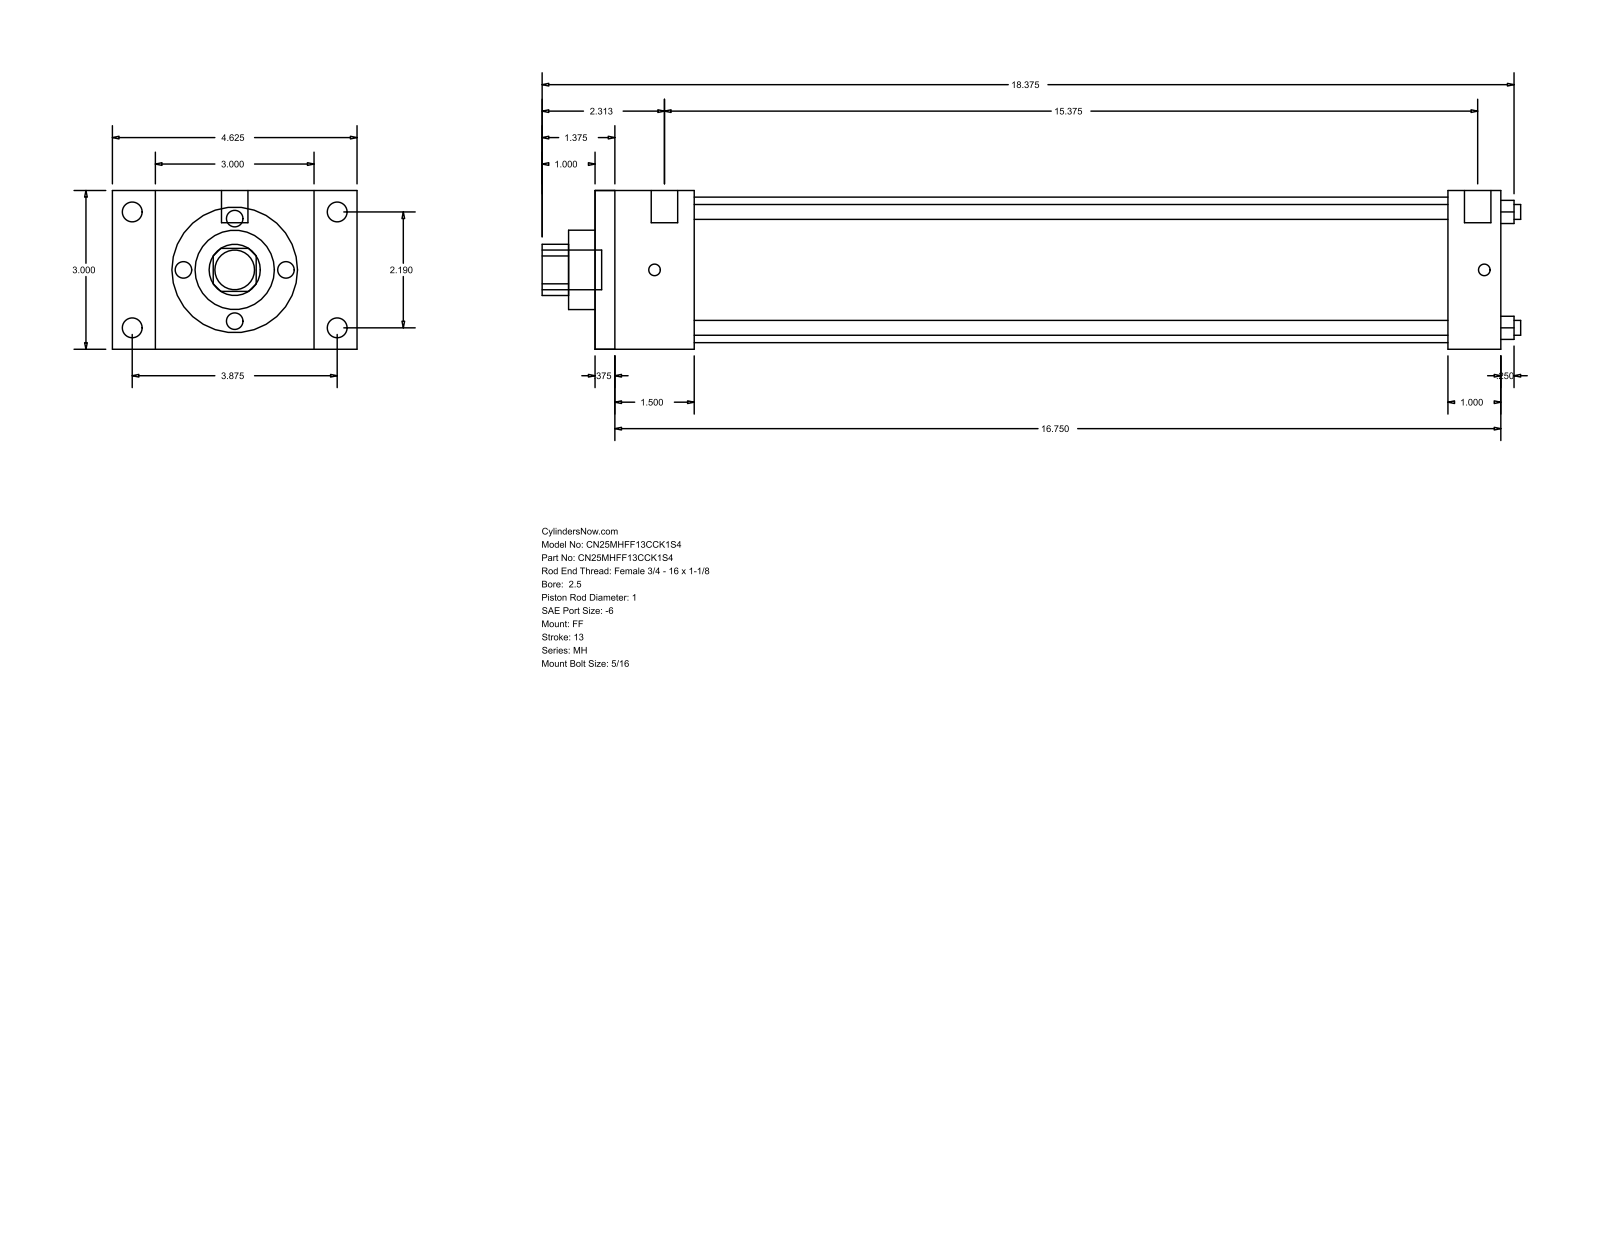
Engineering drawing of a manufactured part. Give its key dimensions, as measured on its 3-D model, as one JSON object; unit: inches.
{"part_name": "MH_FF__0250_1", "step_written_by": "GSSL Pune (CONFIG_CONTROL_DESIGN)", "units": "inches", "bodies": {"solids": 0, "faces": 92, "planar": 64, "cylindrical": 28, "other": 0}, "overall_size": [18.5, 4.625, 3], "round_holes": [[0.281, 4], [1, 1], [1.5, 1], [2.75, 1]], "round_bosses_or_shafts": [[0.375, 4], [0.219, 4], [0.5, 2], [0.75, 1]], "partial_cylinders_radius": [[0.484, 1]], "face_to_face_distances": [3, 17.125, 0.375, 16.75, 1, 1.875, 16.125, 1.5, 15.75, 14.25], "hole_center_spacings": [1.548, 2.19, 3.097]}
